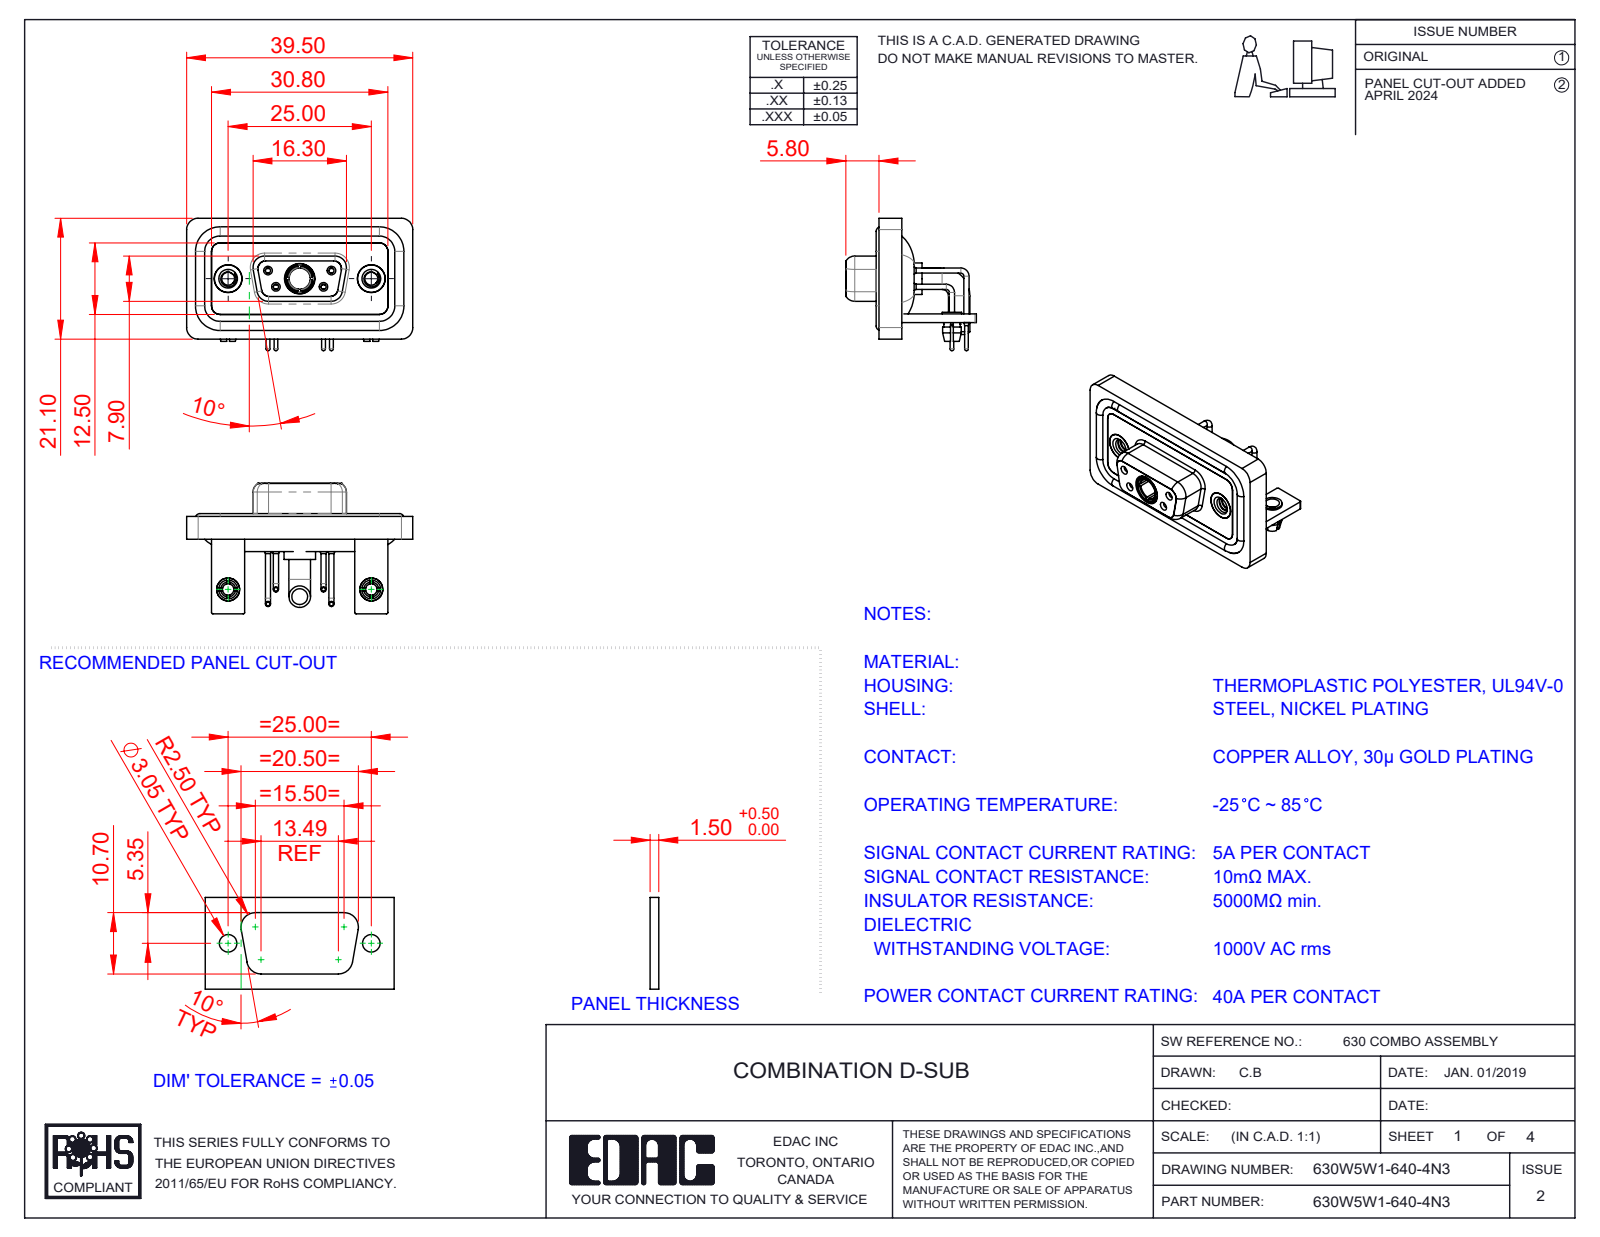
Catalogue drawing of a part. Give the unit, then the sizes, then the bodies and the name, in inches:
Units: inches
Overall size (bounding box): 1.555 × 0.91 × 0.898
Round holes (diameter × count): ⌀0.079 ×6, ⌀0.035 ×4, ⌀0.043 ×4, ⌀0.059 ×4, ⌀0.191 ×3, ⌀0.063 ×2, ⌀0.067 ×2, ⌀0.089 ×2, ⌀0.098 ×2, ⌀0.126 ×2, ⌀0.157 ×2, ⌀0.159 ×2
Round bosses / shafts (diameter × count): ⌀0.063 ×6, ⌀0.035 ×4, ⌀0.026 ×4, ⌀0.195 ×2, ⌀0.189 ×2, ⌀0.157 ×2, ⌀0.148 ×2, ⌀0.134 ×2
Partial cylindrical surfaces — rounded edges, fillets, slot ends (radius × count): R0.079 ×19, R0.059 ×18, R0.01 ×16, R0.053 ×8, R0.063 ×8, R0.02 ×5, R0.024 ×4, R0.026 ×4
Main face-to-face distances: 0.016, 0.114, 0.059, 0.071, 0.043, 0.146, 0.063, 0.031, 0.098, 0.122
Hole centre spacings: 0.124, 0.225, 0.28, 0.492, 0.713, 0.984, 0.173, 0.173
Volume: 0.324 in³ · Surface area: 13.69 in²
Bodies: 17 solids, 816 faces (262 planar, 361 cylindrical, 193 other)
Part name (STEP PRODUCT): 630W5W1-640-4N3; Power Socket_40A RA; 630Combo Contact Row 2_50 Contacts; 630Combo Shell Front_09 Contacts (+7 more)
STEP written by: SolidWorks 2023 (CONFIG_CONTROL_DESIGN)
